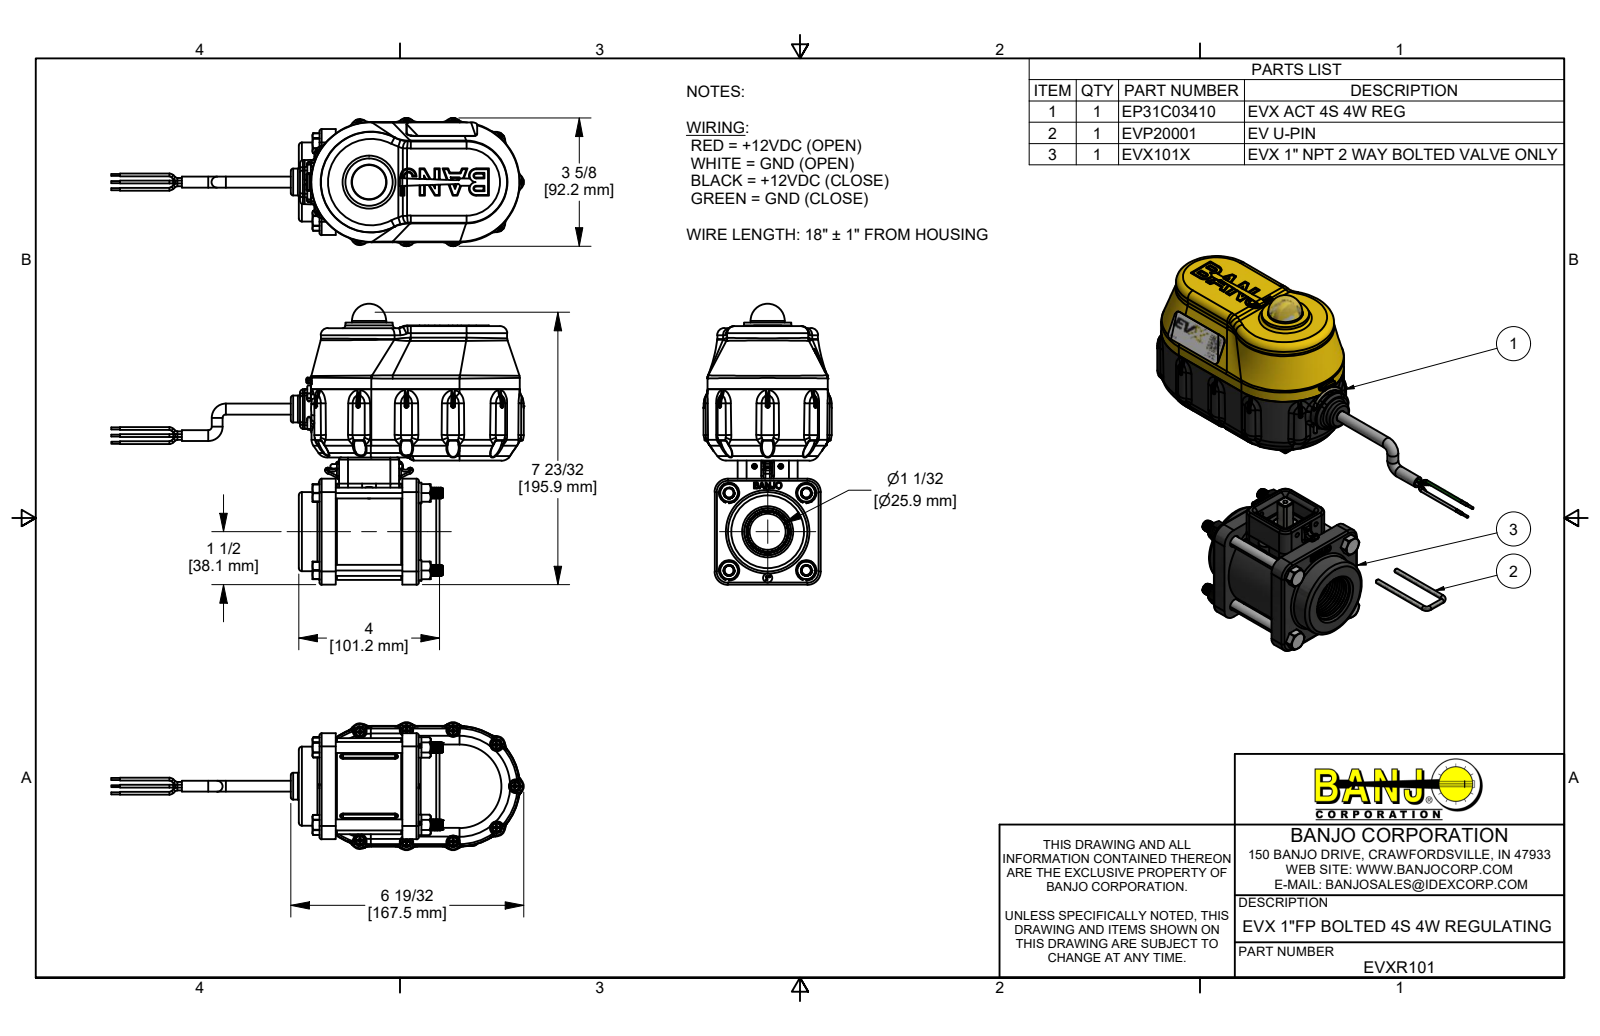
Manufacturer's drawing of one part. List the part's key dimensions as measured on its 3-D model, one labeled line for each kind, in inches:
Part name (STEP PRODUCT): EVXR101; EVP20001; EP31C03410; 91400A119 (+8 more)
STEP written by: Autodesk Inventor 2019 (AUTOMOTIVE_DESIGN)
Units: inches
Bodies: 95 solids, 12837 faces (3644 planar, 3437 cylindrical, 5756 other)
Overall size (bounding box): 38.771 × 7.957 × 3.63
Volume: 50.24 in³ · Surface area: 742.6 in²
Round holes (diameter × count): ⌀0.15 ×13, ⌀0.095 ×11, ⌀0.107 ×4, ⌀0.126 ×4, ⌀0.136 ×4, ⌀0.17 ×4, ⌀0.252 ×4, ⌀0.322 ×4, ⌀0.35 ×4, ⌀0.135 ×3, ⌀1.02 ×3, ⌀0.089 ×2
Round bosses / shafts (diameter × count): ⌀0.268 ×60, ⌀0.08 ×20, ⌀0.25 ×17, ⌀0.14 ×11, ⌀0.108 ×11, ⌀0.085 ×11, ⌀0.058 ×8, ⌀0.313 ×5
Partial cylindrical surfaces — rounded edges, fillets, slot ends (radius × count): R0.04 ×147, R0.02 ×84, R0.06 ×62, R0.01 ×56, R0.005 ×41, R0.03 ×32, R0.08 ×28, R0.1 ×22
Main face-to-face distances: 0.1, 2.565, 0.46, 2.345, 0.055, 0.125, 1.685, 0.78, 2.465, 0.09
Hole centre spacings: 1.55, 2.192, 1.046, 1.662, 1.891, 2.73, 3.186, 3.296
